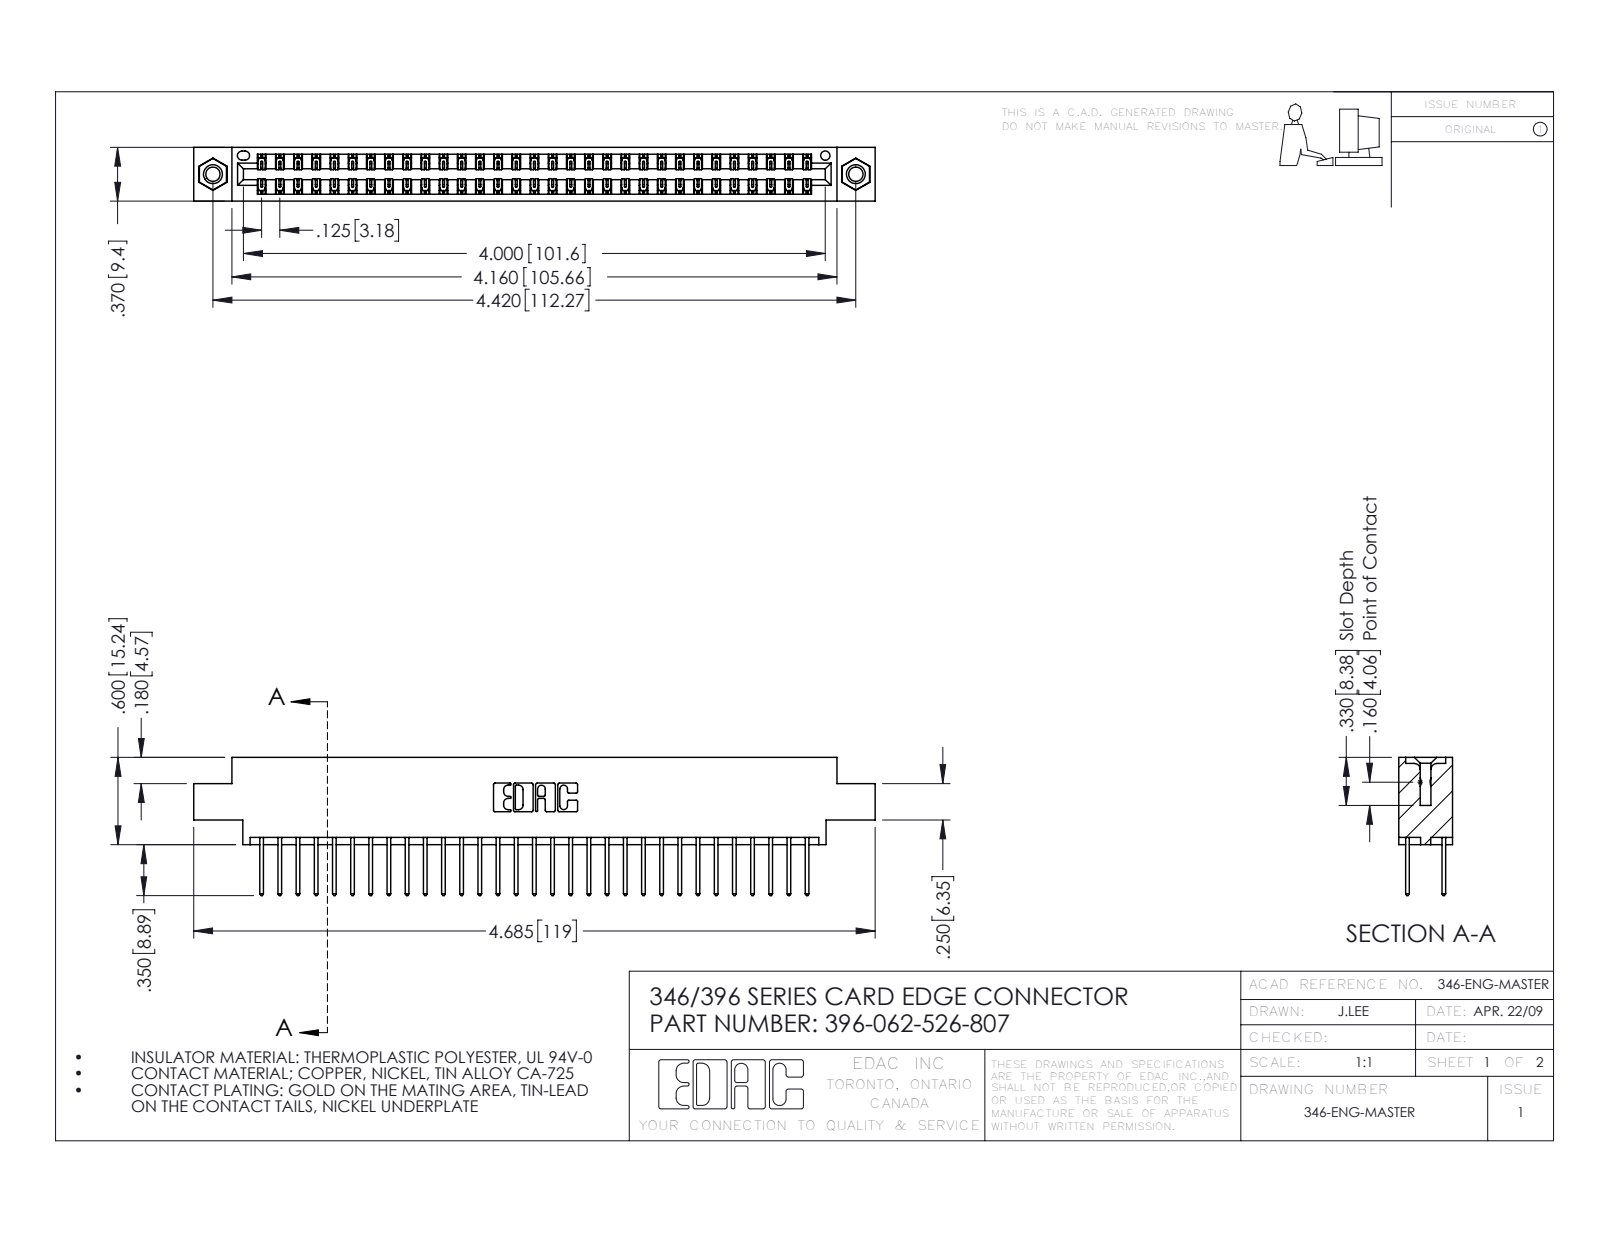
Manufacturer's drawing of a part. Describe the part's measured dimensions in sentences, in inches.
The part is named "346 Part_0.170 Offset - 0.156 Dia-TI; 345-250-001_345-250-005-103; 345-292-001_345-293-126; 396-062-526-807". Its 3-D file was written by "SolidWorks 2016 (CONFIG_CONTROL_DESIGN)". It is 65 solids with 3410 faces: 2282 planar, 1112 cylindrical and 16 other. Overall it measures 4.685 by 0.95 by 0.37 inches. Its volume is 0.699 cubic inches and its surface area 25.17 square inches. Round holes: 2 of diameter 0.098, 2 of diameter 0.125, 2 of diameter 0.156, 1 of diameter 0.064. Round bosses or shafts: 2 of diameter 0.155. Partial cylindrical surfaces (rounded edges, fillets, slot ends): 93 of radius 0.006, 62 of radius 0.01, 22 of radius 0.01, 6 of radius 0.007, 6 of radius 0.031, 3 of radius 0.026, 2 of radius 0.014, 2 of radius 0.022. The main face-to-face distances are 0.048, 0.322, 0.25, 0.37, 0.072, 0.298, 0.025, 0.275, 0.222, 0.148. The hole center spacings are 0.246, 4.212, 4.42.
